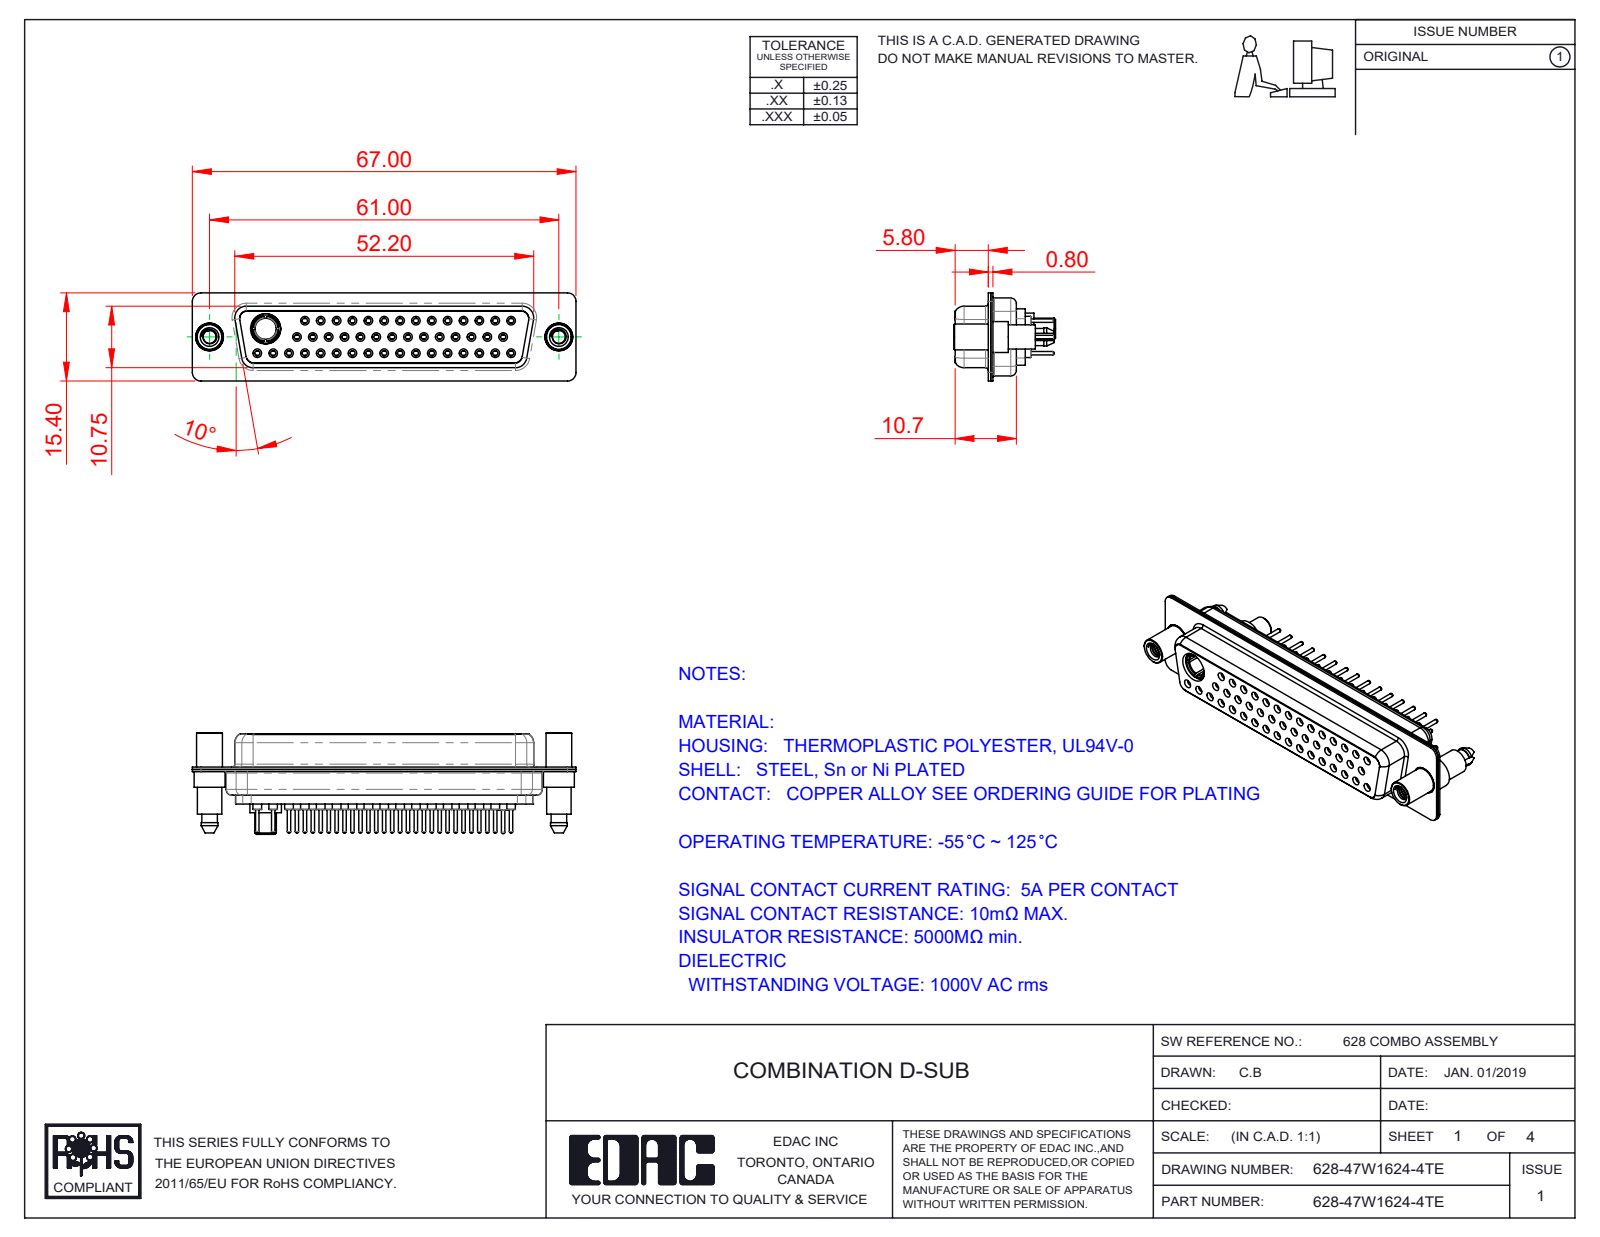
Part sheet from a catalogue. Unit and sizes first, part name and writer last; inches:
Units: inches
Overall size (bounding box): 2.638 × 0.699 × 0.606
Round holes (diameter × count): ⌀0.043 ×46, ⌀0.035 ×45, ⌀0.059 ×45, ⌀0.079 ×45, ⌀0.063 ×31, ⌀0.067 ×14, ⌀0.191 ×3, ⌀0.089 ×2, ⌀0.157 ×2, ⌀0.159 ×2, ⌀0.146 ×1, ⌀0.209 ×1
Round bosses / shafts (diameter × count): ⌀0.087 ×46, ⌀0.024 ×46, ⌀0.063 ×15, ⌀0.213 ×2, ⌀0.195 ×2, ⌀0.189 ×2, ⌀0.177 ×2, ⌀0.167 ×2
Partial cylindrical surfaces — rounded edges, fillets, slot ends (radius × count): R0.059 ×18, R0.053 ×12, R0.079 ×12, R0.063 ×10, R0.01 ×4, R0.02 ×4, R0.024 ×4, R0.026 ×4
Main face-to-face distances: 0.016, 0.446, 0.238, 0.254, 0.074, 0.482, 0.244, 0.228, 0.407, 0.43
Hole centre spacings: 0.124, 0.109, 0.218, 0.327, 0.436, 0.545, 0.654, 0.763
Volume: 0.454 in³ · Surface area: 23.5 in²
Bodies: 53 solids, 2929 faces (801 planar, 1062 cylindrical, 1066 other)
Part name (STEP PRODUCT): 628-47W1624-4TE; 628Combo Shell Rear_50 Contacts; 628Combo Contact Row 1_24; Power Socket_40A S (+5 more)
STEP written by: SolidWorks 2016 (CONFIG_CONTROL_DESIGN)
